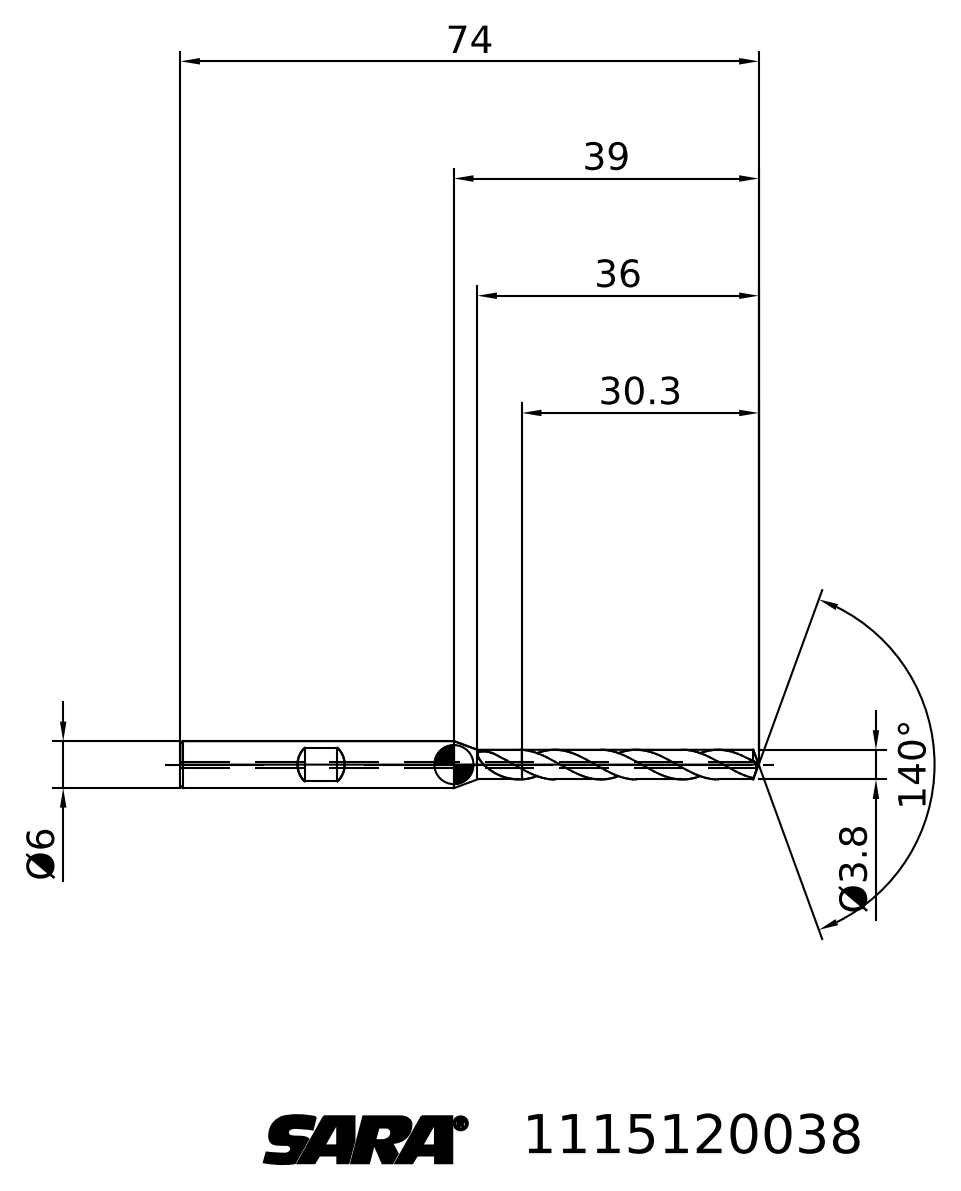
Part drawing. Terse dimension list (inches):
written by: TDM (AUTOMOTIVE_DESIGN)
unit: in
bodies: 2 solids, 30 faces (6 planar, 0 cylindrical, 24 other)
size: 2.913 × 0.394 × 0.236
volume: 0.079 in³; area: 1.891 in²
face distances: 1.72
